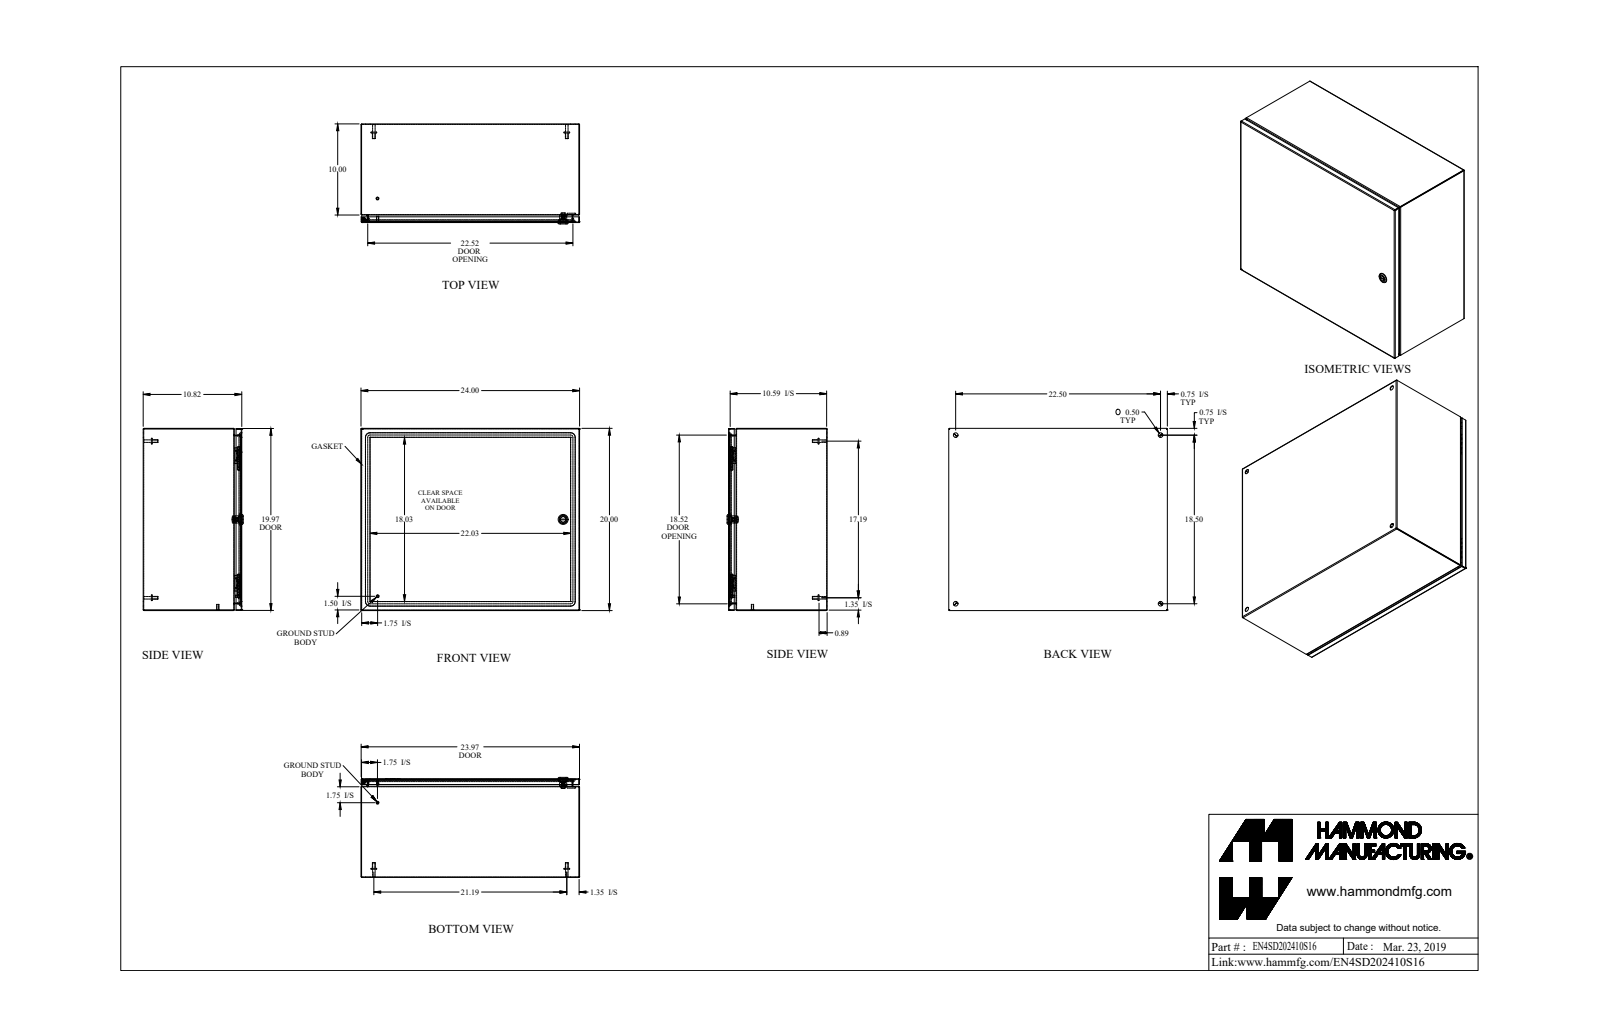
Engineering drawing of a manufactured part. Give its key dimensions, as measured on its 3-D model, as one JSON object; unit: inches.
{"part_name": "EN4SD202410S16_Default", "step_written_by": "SolidWorks 2019 (CONFIG_CONTROL_DESIGN)", "units": "inches", "bodies": {"solids": 22, "faces": 656, "planar": 303, "cylindrical": 211, "other": 142}, "overall_size": [24, 20, 10.981], "volume_in3": 123.2, "surface_area_in2": 4219, "round_holes": [[0.5, 5], [0.172, 1], [0.197, 1], [0.24, 1], [0.242, 1], [0.387, 1], [0.63, 1], [0.768, 1]], "round_bosses_or_shafts": [[0.313, 6], [0.625, 5], [0.275, 4], [0.25, 2], [1.1, 1], [0.785, 1], [0.525, 1], [0.475, 1]], "partial_cylinders_radius": [[0.029, 21], [0.086, 21], [0.188, 12], [0.006, 4], [0.062, 4], [0.25, 4], [0.499, 4], [0.125, 2]], "face_to_face_distances": [0.057, 0.057, 10.707, 10.764, 10.764, 10.821, 19.943, 23.943, 19.886, 20], "hole_center_spacings": [9.31, 18.5, 22.5, 23.351, 29.129]}
